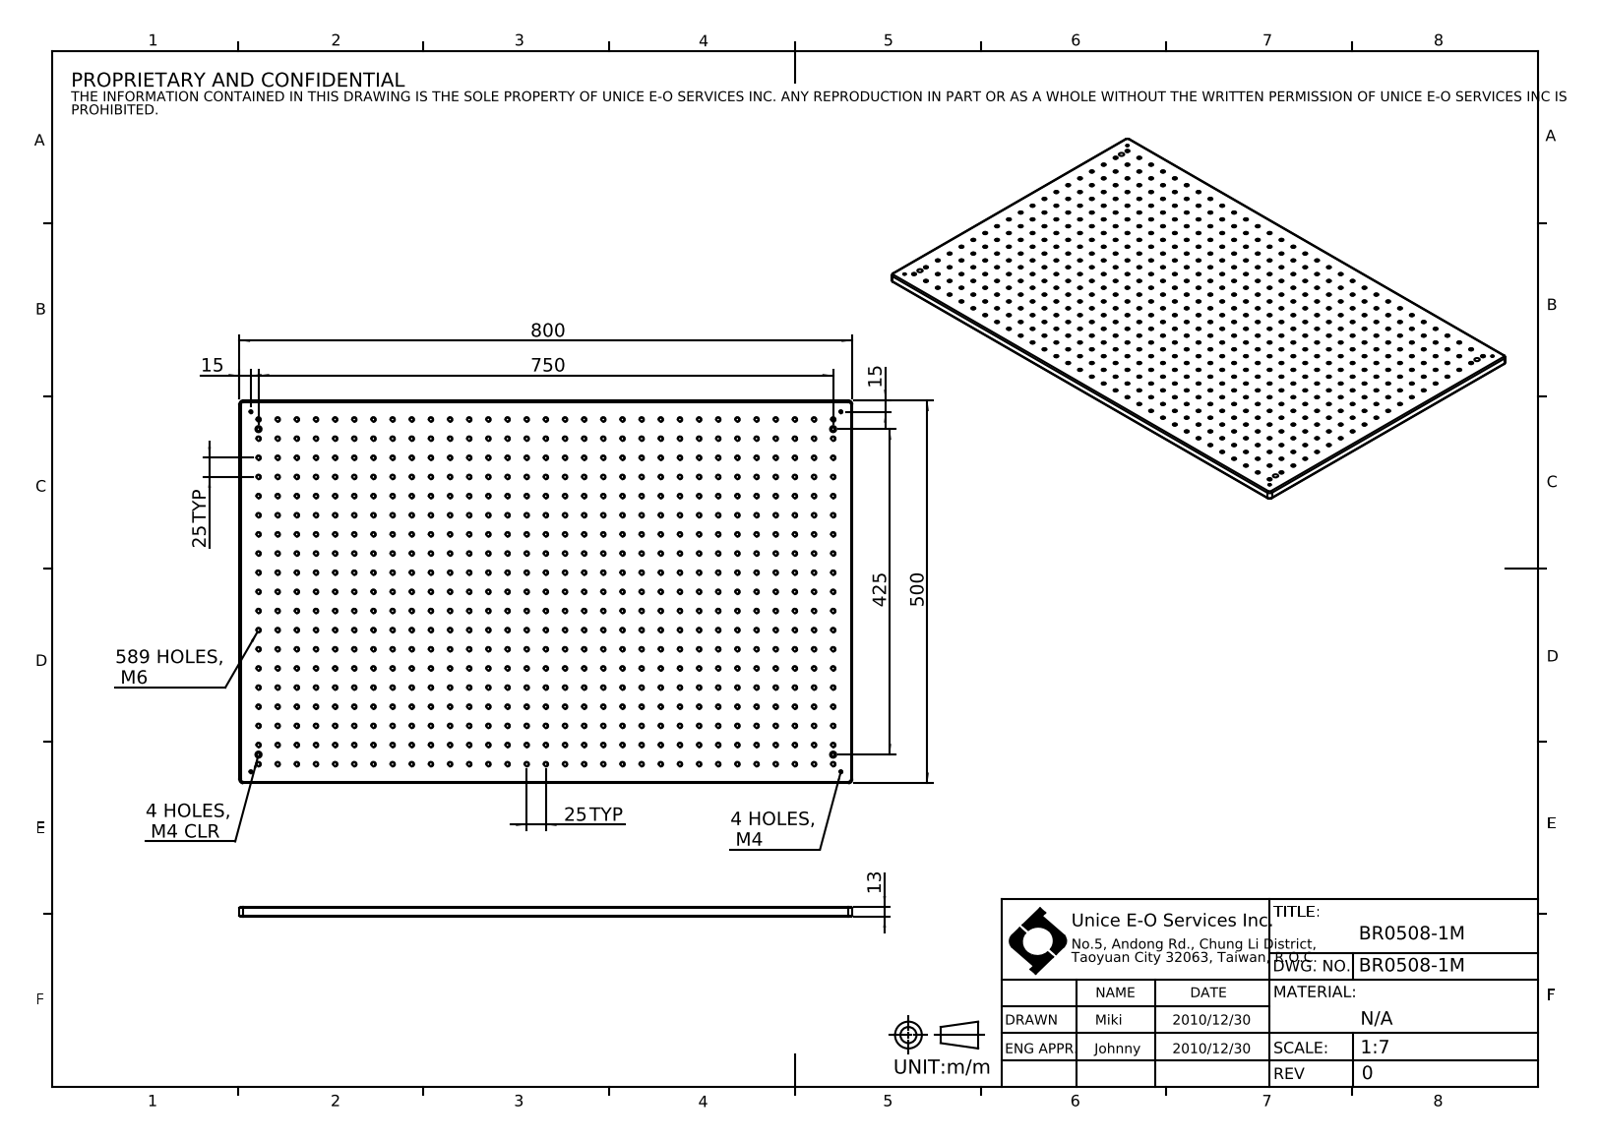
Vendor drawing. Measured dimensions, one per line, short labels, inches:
name: BR0508-1M
written by: SolidWorks 2016 (CONFIG_CONTROL_DESIGN)
unit: in
bodies: 1 solid, 1232 faces (10 planar, 1214 cylindrical, 8 other)
size: 31.496 × 19.685 × 0.512
volume: 307.7 in³; area: 1 438 in²
holes: 589× ⌀0.197, 4× ⌀0.13, 4× ⌀0.177, 4× ⌀0.315
rounds: 8× R0.079, 4× R0.197
face distances: 0.512, 19.685, 31.496, 0.276, 0.236
hole spacings: 0.984, 1.969, 2.953, 3.937, 4.921, 5.906, 6.89, 7.874
